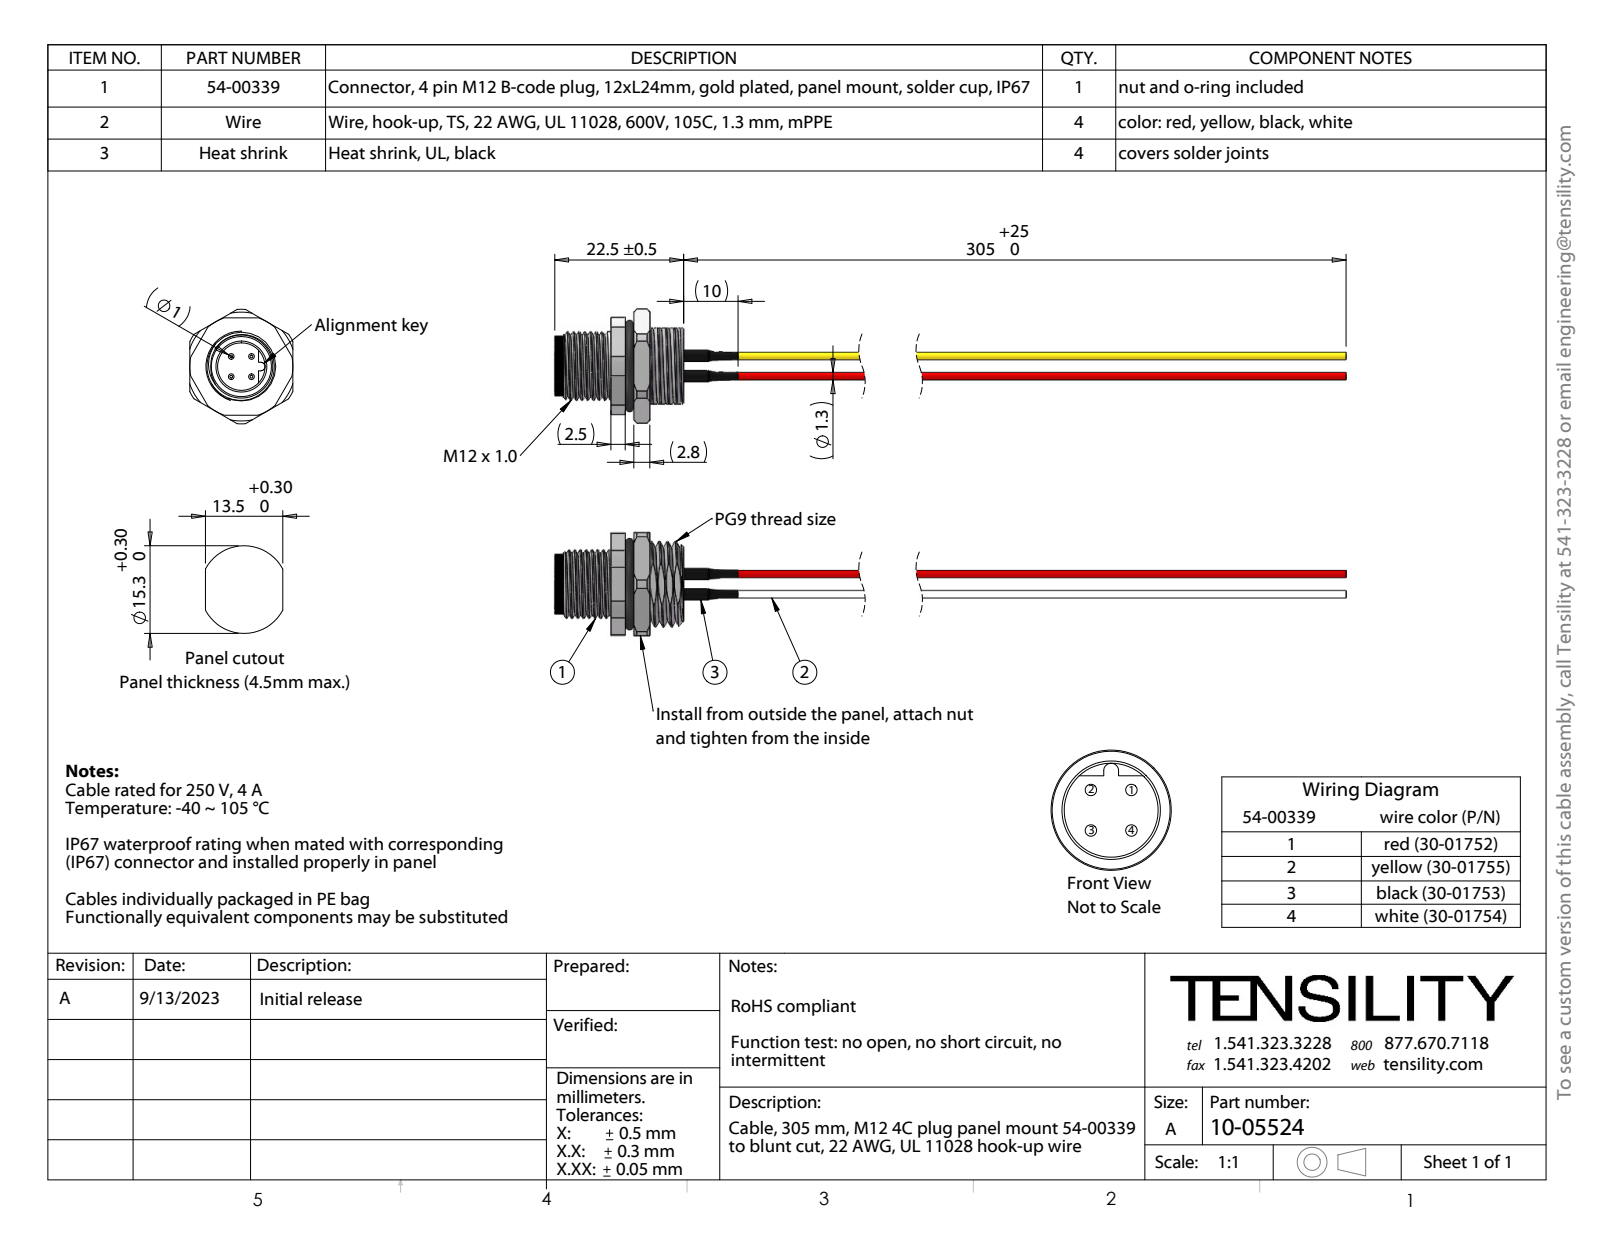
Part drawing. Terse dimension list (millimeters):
name: 54-00339-05; 30-01752_blunt cut; 54-00339; 54-00339-02 (+8 more)
written by: SolidWorks 2021 (CONFIG_CONTROL_DESIGN)
unit: mm
bodies: 84 solids, 784 faces (235 planar, 432 cylindrical, 117 other)
size: 174.3 × 20 × 18
volume: 3 878 mm³; area: 18 180 mm²
holes: 4× ⌀0.8, 4× ⌀1, 1× ⌀8, 1× ⌀8.3, 1× ⌀9.3, 1× ⌀11, 1× ⌀14
bosses: 4× ⌀2, 4× ⌀1.4, 4× ⌀1.3, 1× ⌀13, 1× ⌀12, 1× ⌀10.5, 1× ⌀9
rounds: 2× R1.96, 1× R0.75, 1× R7.5, 1× R9, 1× R10
face distances: 6.5, 1.5, 12.2, 2.5, 4, 1.7, 8.2, 5.7, 9.7, 3.2
hole spacings: 0.32, 0.48, 0.37, 0.31, 0.45, 0.33, 0.39, 4.72
